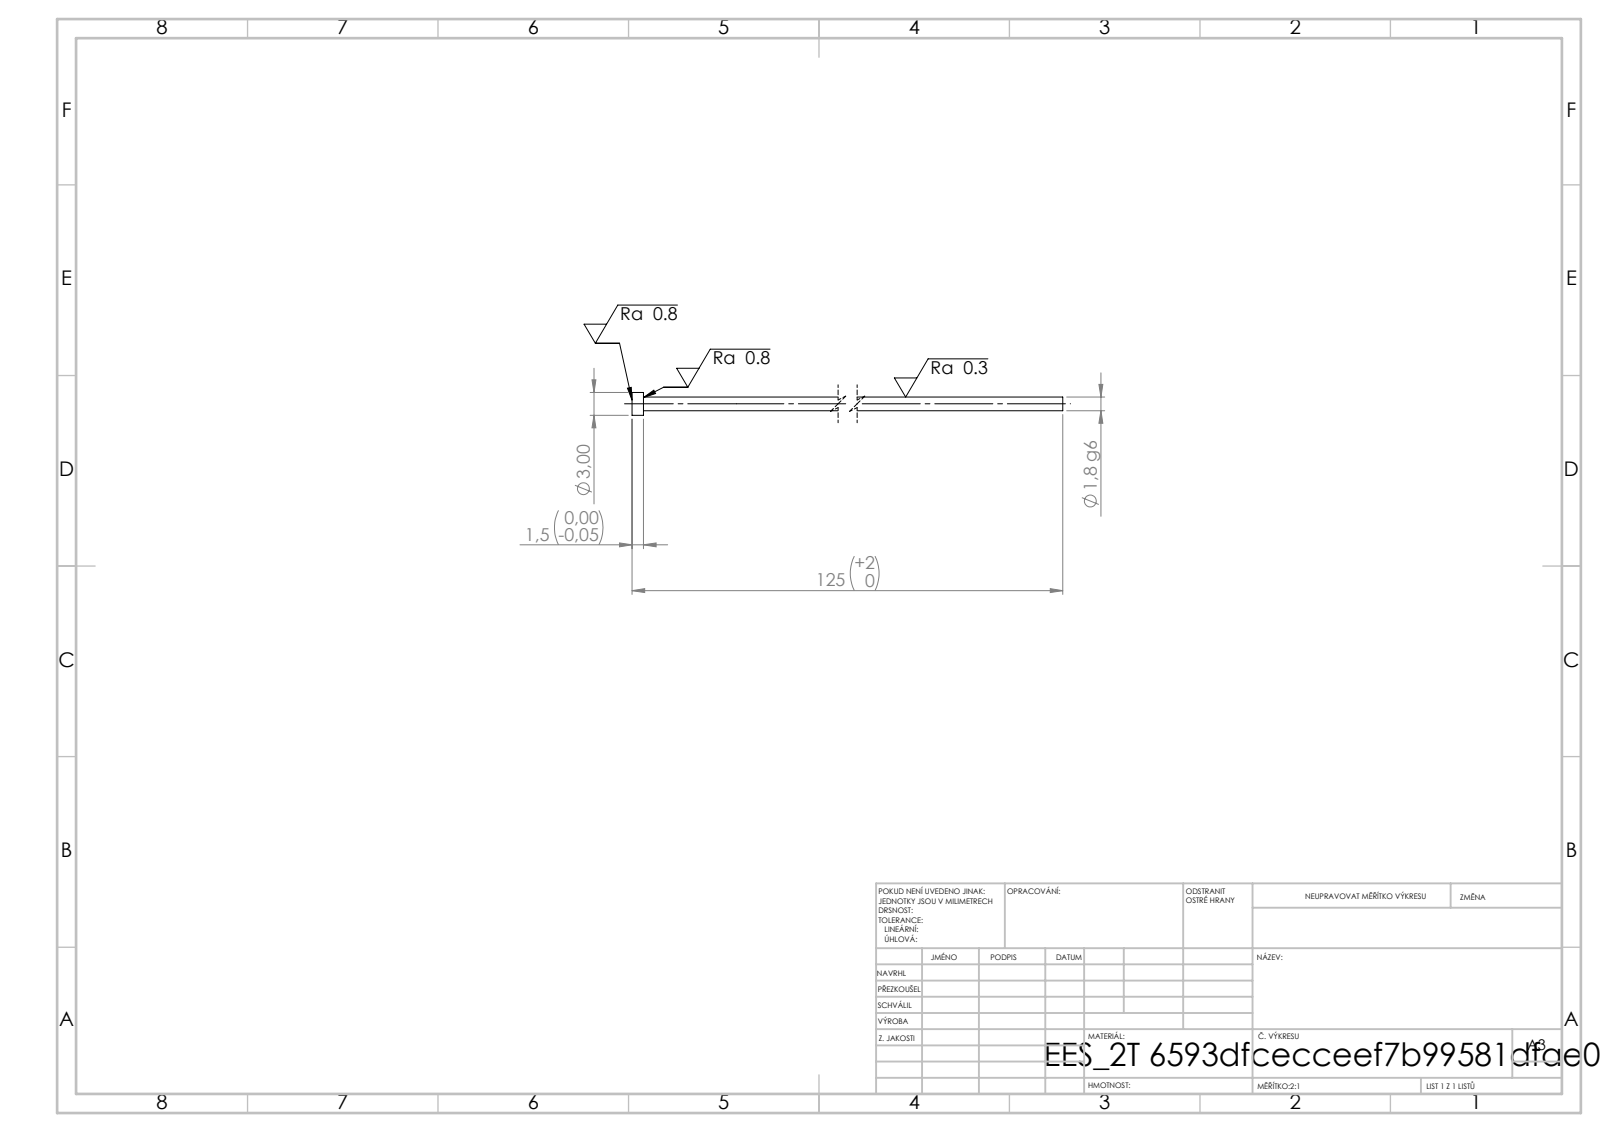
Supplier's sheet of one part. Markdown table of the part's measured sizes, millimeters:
| quantity | value |
| --- | --- |
| STEP written by | SolidWorks 2019 (CONFIG_CONTROL_DESIGN) |
| units | millimeters |
| bodies | 1 solid, 7 faces (3 planar, 4 cylindrical, 0 other) |
| overall size | 125 × 3 × 3 |
| volume | 325 mm³ |
| surface area | 727 mm² |
| round bosses / shafts (diameter × count) | 3 × 1, 1.8 × 1 |
| main face-to-face distances | 1.5, 125, 123.5 |
